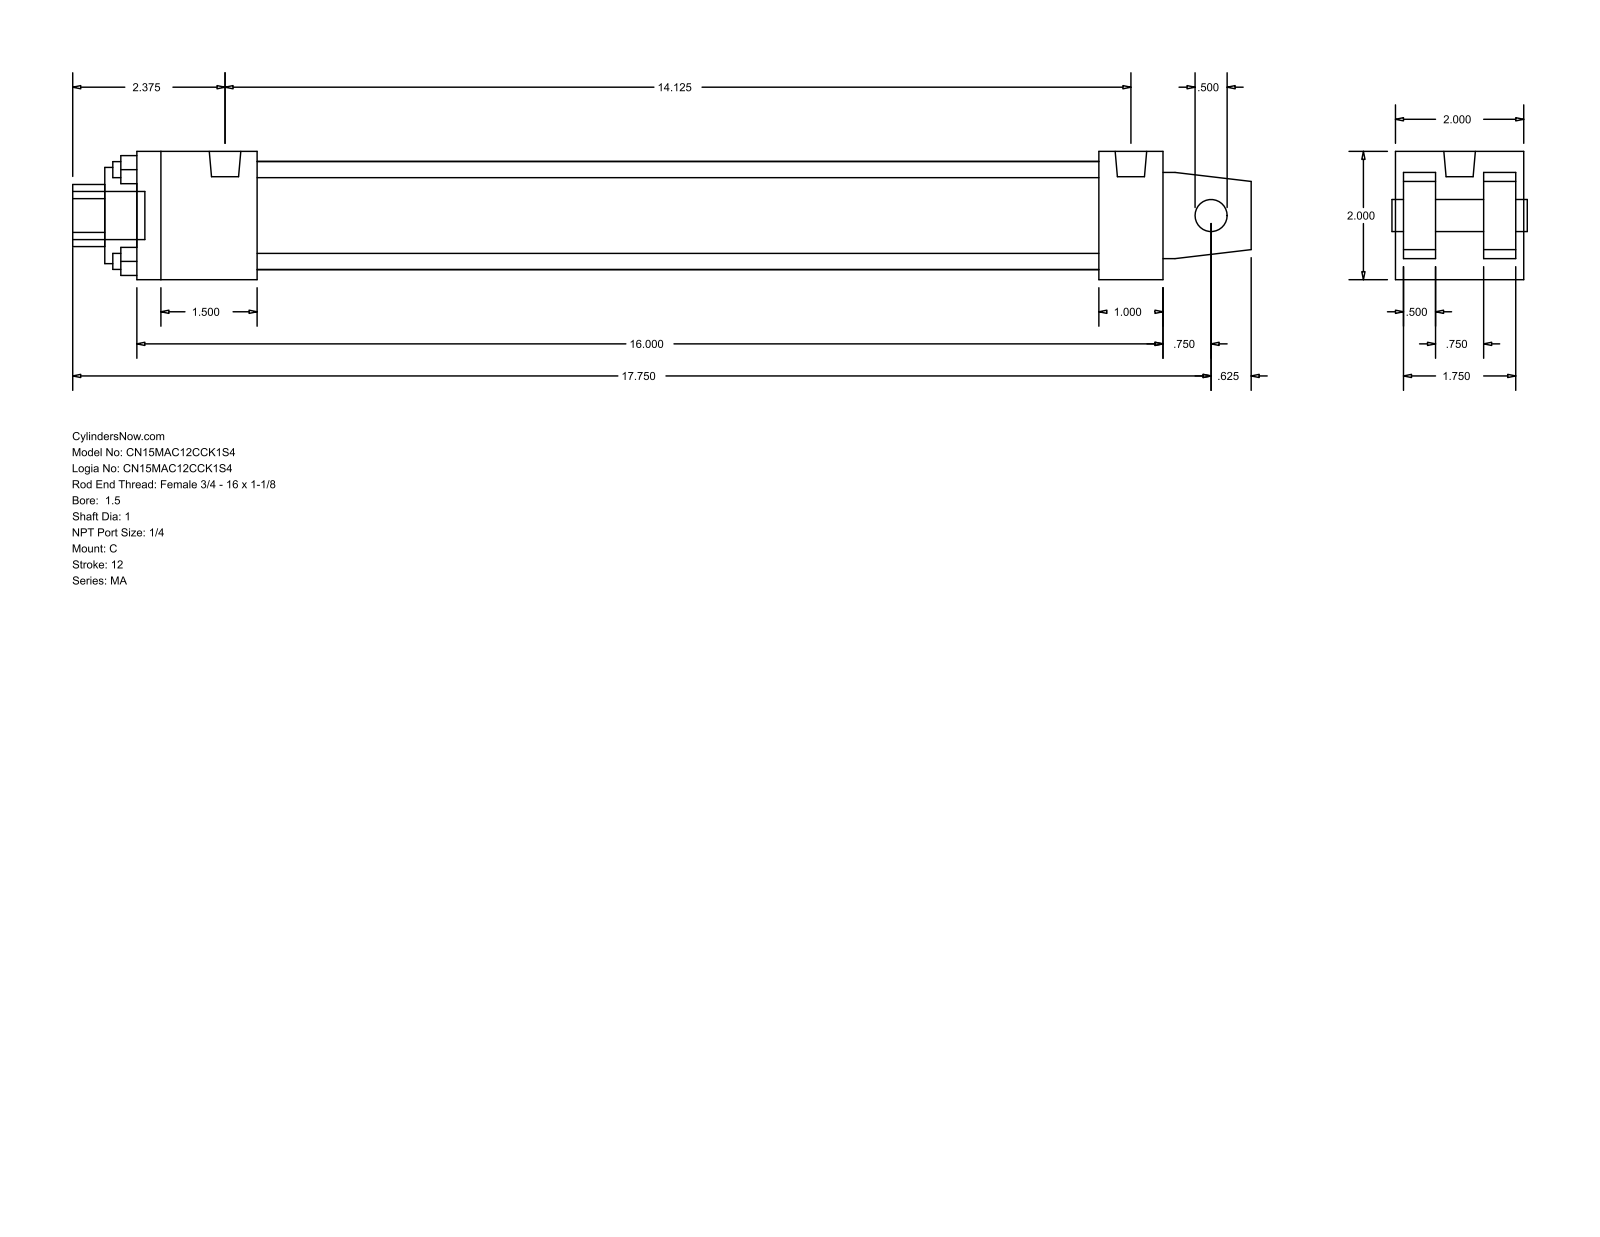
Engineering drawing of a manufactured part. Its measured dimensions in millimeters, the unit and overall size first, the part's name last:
Units: millimetres
Overall size (bounding box): 466.73 × 50.8 × 50.8
Round holes (diameter × count): ⌀6.35 ×4, ⌀12.7 ×1, ⌀25.4 ×1, ⌀38.1 ×1, ⌀42.93 ×1
Round bosses / shafts (diameter × count): ⌀7.94 ×4, ⌀12.49 ×2, ⌀19.05 ×1
Partial cylindrical surfaces — rounded edges, fillets, slot ends (radius × count): R12.29 ×1
Main face-to-face distances: 50.8, 47.63, 12.7, 34.93, 3.17, 15.87, 31.76, 60.33, 393.7, 44.46
Hole centre spacings: 25.68, 36.32, 51.36
Bodies: 0 solids, 103 faces (76 planar, 27 cylindrical, 0 other)
Part name (STEP PRODUCT): MA_C__0150_1
STEP written by: GSSL Pune (CONFIG_CONTROL_DESIGN)
